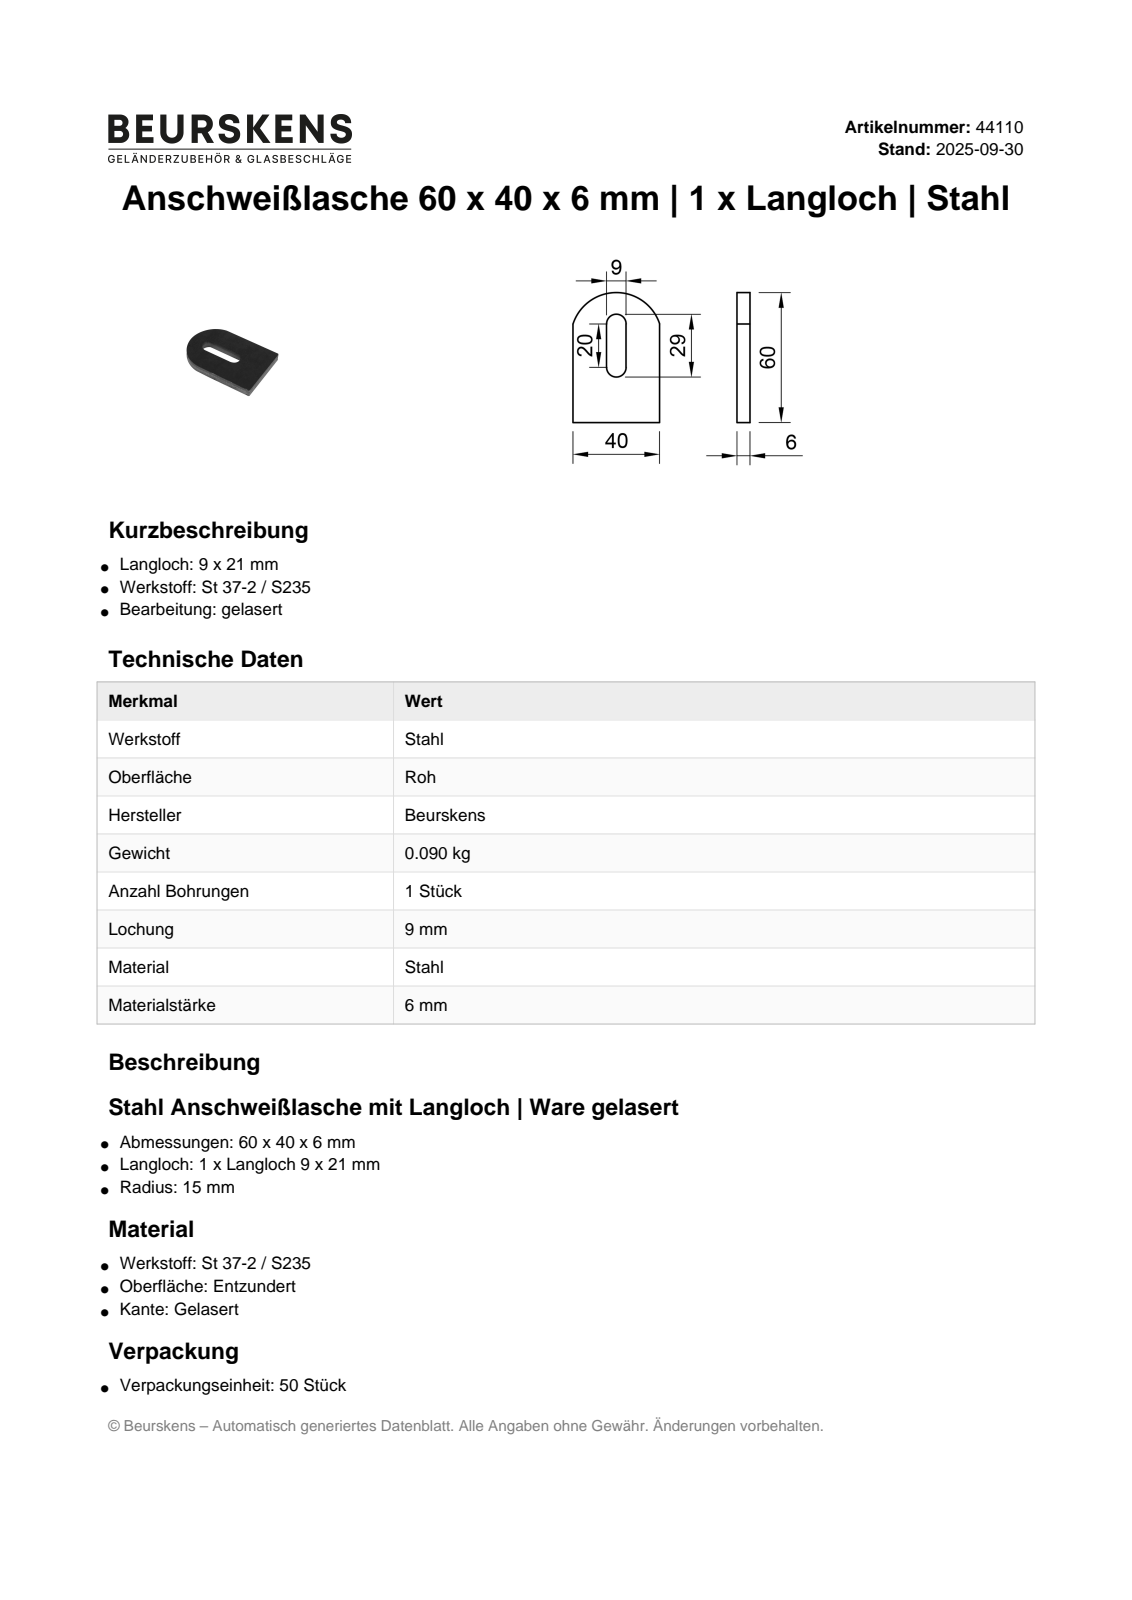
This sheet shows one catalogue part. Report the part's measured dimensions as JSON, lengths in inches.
{"part_name": "44110", "step_written_by": "Autodesk Inventor 2023 (AUTOMOTIVE_DESIGN)", "units": "inches", "bodies": {"solids": 1, "faces": 10, "planar": 7, "cylindrical": 3, "other": 0}, "overall_size": [2.362, 1.575, 0.236], "volume_in3": 0.733, "surface_area_in2": 8.548, "partial_cylinders_radius": [[0.177, 2], [0.828, 1]], "face_to_face_distances": [0.236, 1.575, 0.61, 0.965, 0.354]}
